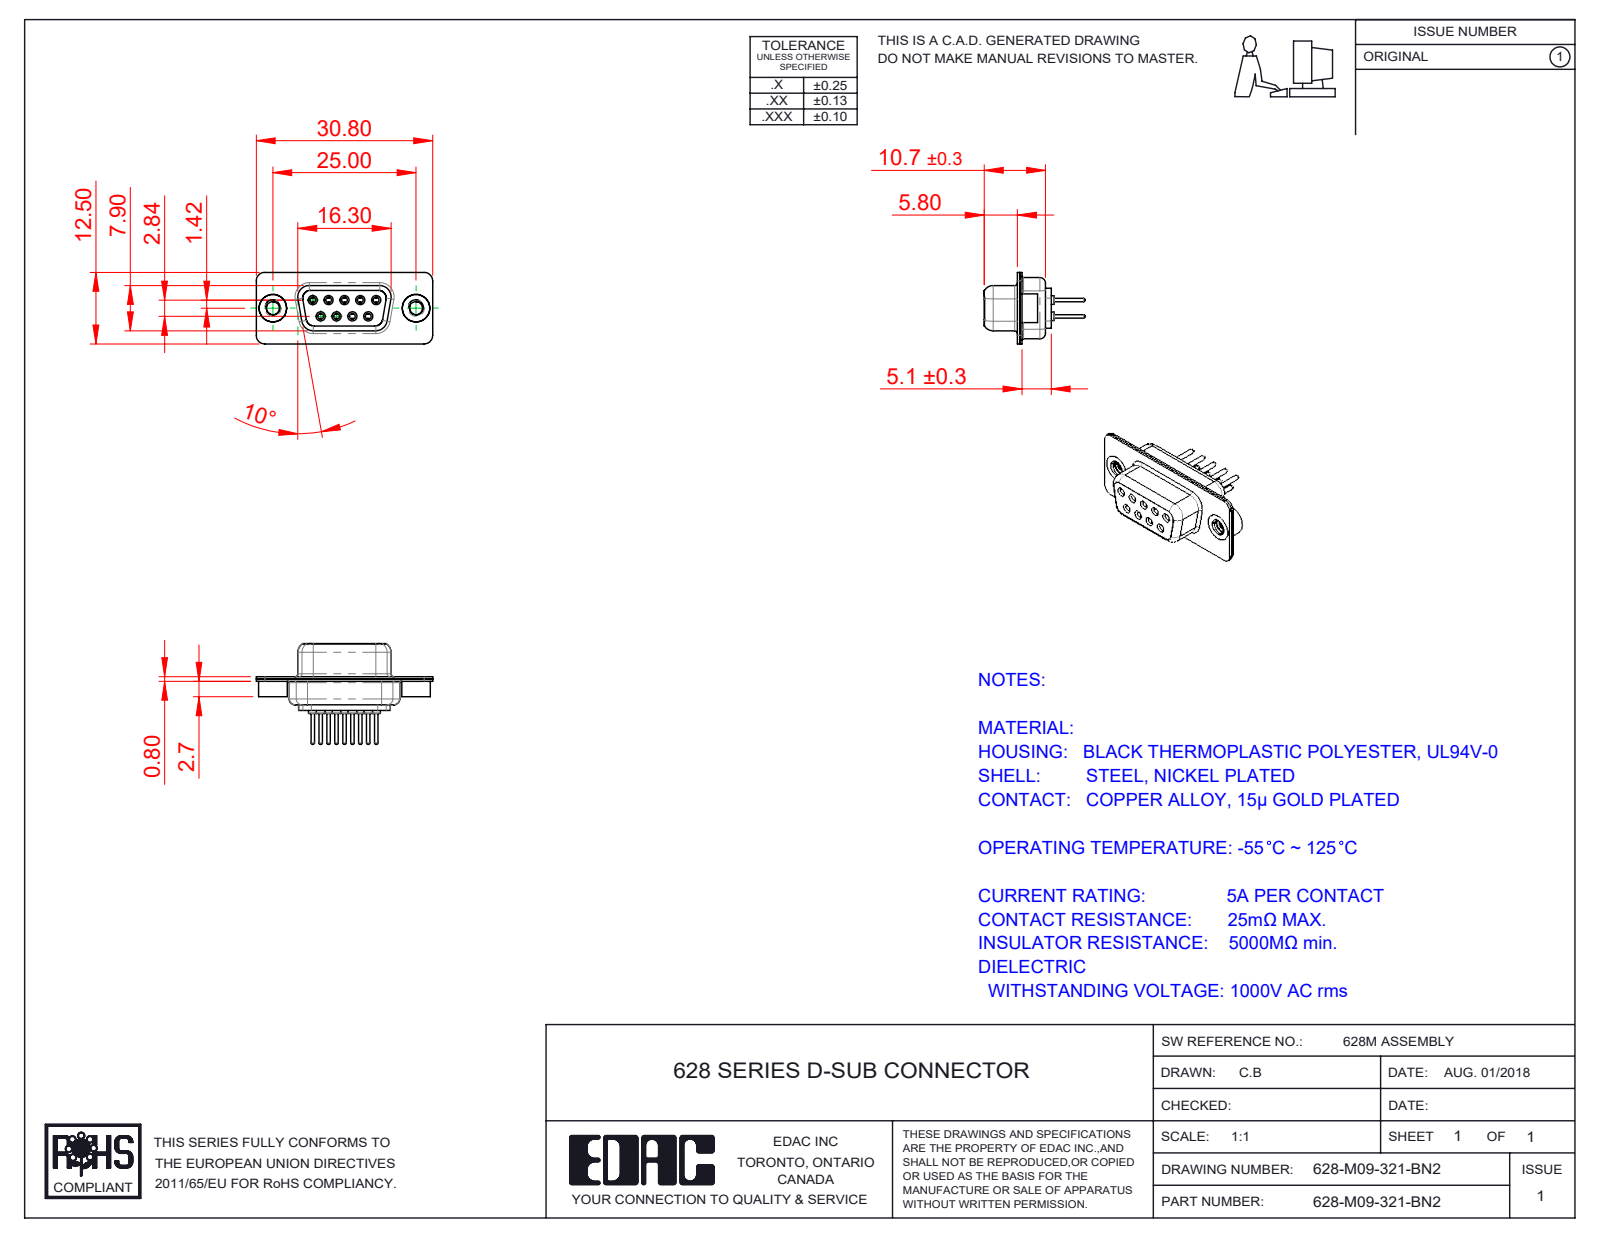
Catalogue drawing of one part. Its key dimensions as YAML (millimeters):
part_name: "628M 4-40 Threaded Rivet; 628-M09-321-BN2; 628M Shell Rear_09 Contacts; 628M Housing_09 Contacts (+3 more)"
step_written_by: "SolidWorks 2020 (CONFIG_CONTROL_DESIGN)"
units: millimeters
bodies: {solids: 14, faces: 774, planar: 202, cylindrical: 308, other: 264}
overall_size: [30.8, 17.6, 12.5]
volume: 1704
surface_area: 4427
round_holes:
  - {diameter: 1, count: 9}
  - {diameter: 1.1, count: 9}
  - {diameter: 1.7, count: 9}
  - {diameter: 1.8, count: 9}
  - {diameter: 2, count: 9}
  - {diameter: 2.26, count: 2}
  - {diameter: 4, count: 2}
  - {diameter: 4.8, count: 2}
round_bosses_or_shafts:
  - {diameter: 2.2, count: 9}
  - {diameter: 1.6, count: 9}
  - {diameter: 1.5, count: 9}
  - {diameter: 0.6, count: 9}
  - {diameter: 5, count: 2}
  - {diameter: 4.9, count: 2}
partial_cylinders:
  - {radius: 1.5, count: 16}
  - {radius: 2, count: 12}
  - {radius: 1.35, count: 8}
  - {radius: 1.6, count: 8}
  - {radius: 0.25, count: 4}
  - {radius: 0.5, count: 4}
  - {radius: 0.6, count: 4}
  - {radius: 0.65, count: 4}
face_to_face_distances: [0.4, 1.4, 0.45, 8.45, 0.8, 1, 8.9, 1.8, 6.2, 7.05]
hole_center_spacings: [3.16, 2.77, 5.54, 5.03, 5.04, 8.31, 7.1, 7.48]
